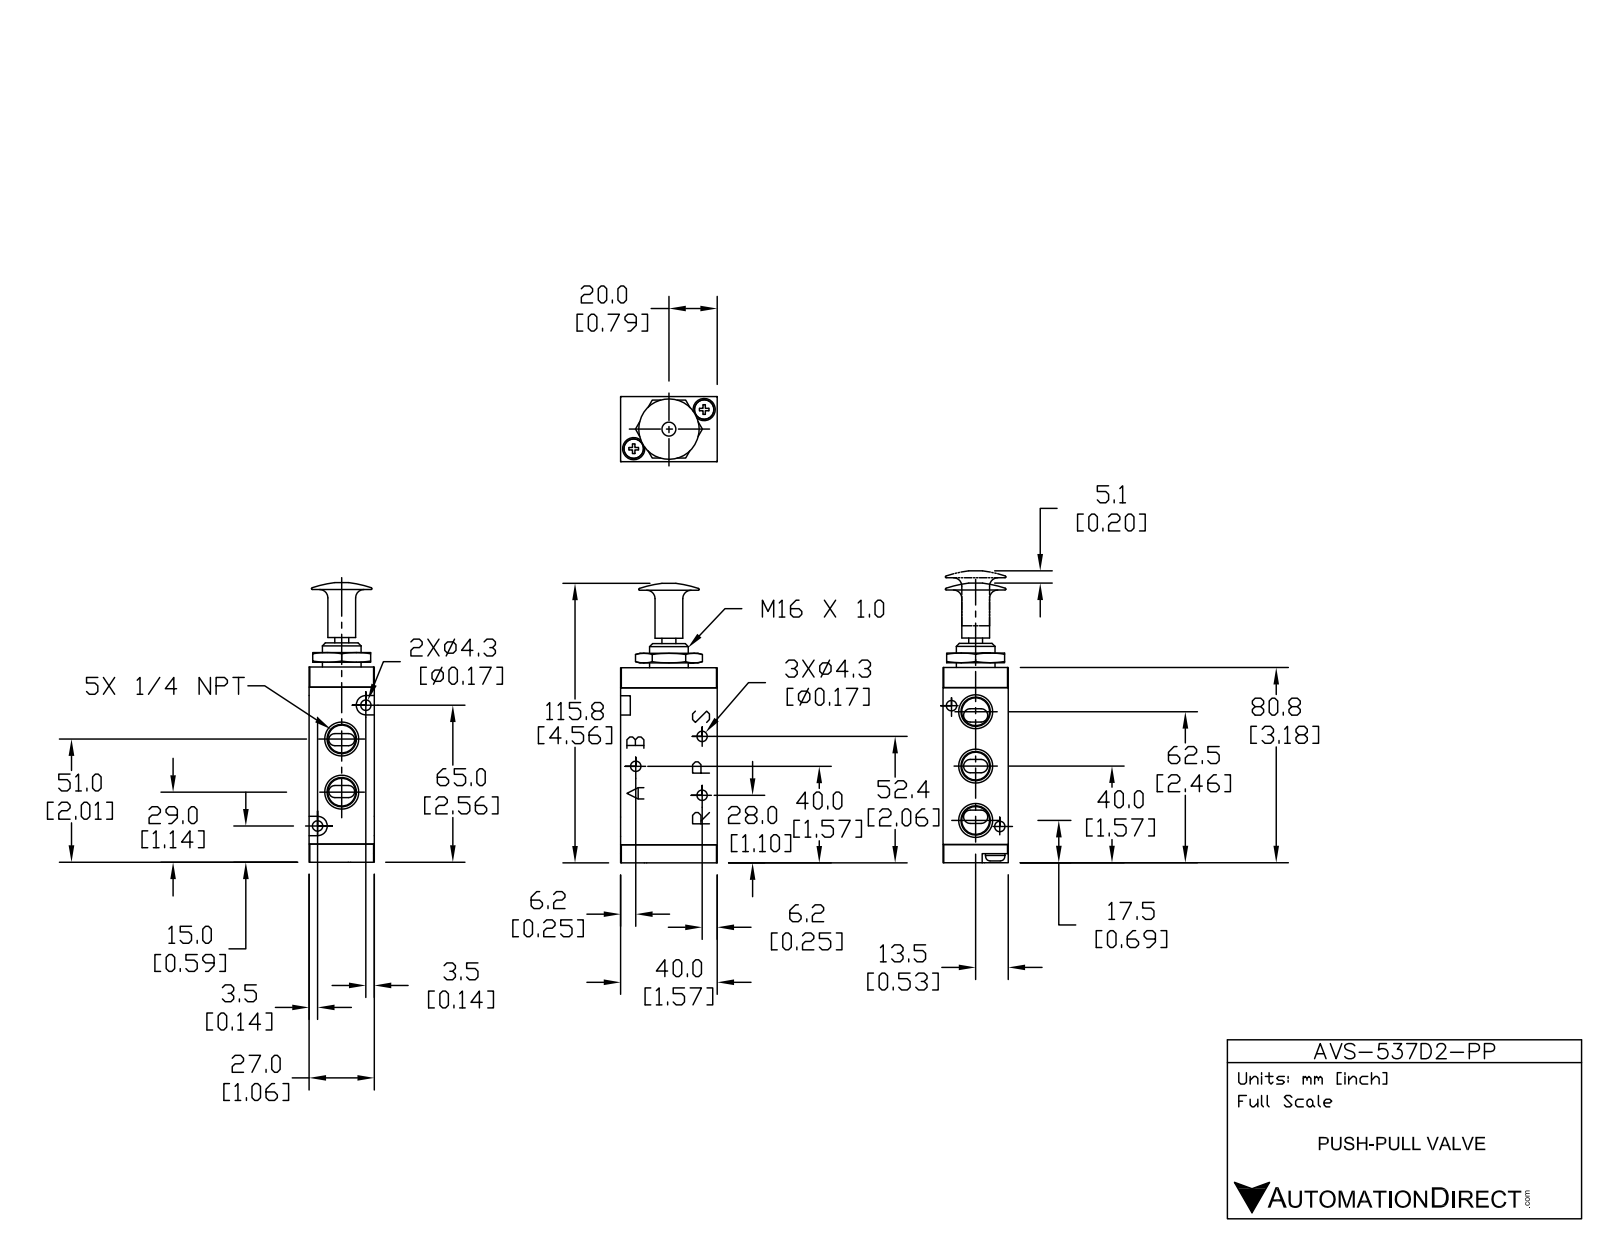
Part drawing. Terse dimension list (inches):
name: AVS-537D2-PP
written by: SolidWorks 2015 (CONFIG_CONTROL_DESIGN)
unit: in
bodies: 4 solids, 252 faces (140 planar, 62 cylindrical, 50 other)
size: 4.528 × 1.575 × 1.063
volume: 5.023 in³; area: 39.71 in²
holes: 5× ⌀0.169, 2× ⌀0.361, 1× ⌀0.226
bosses: 4× ⌀0.319, 4× ⌀0.315, 1× ⌀0.984, 1× ⌀0.63, 1× ⌀0.453
rounds: 6× R0.108, 4× R0.098, 2× R0.039, 2× R0.157
face distances: 1.063, 2.559, 1.575, 0.295, 2.854, 0.327, 3.181, 2.886, 0.157, 0.945
hole spacings: 0.657, 1.181, 0.945, 1.315, 2.12
